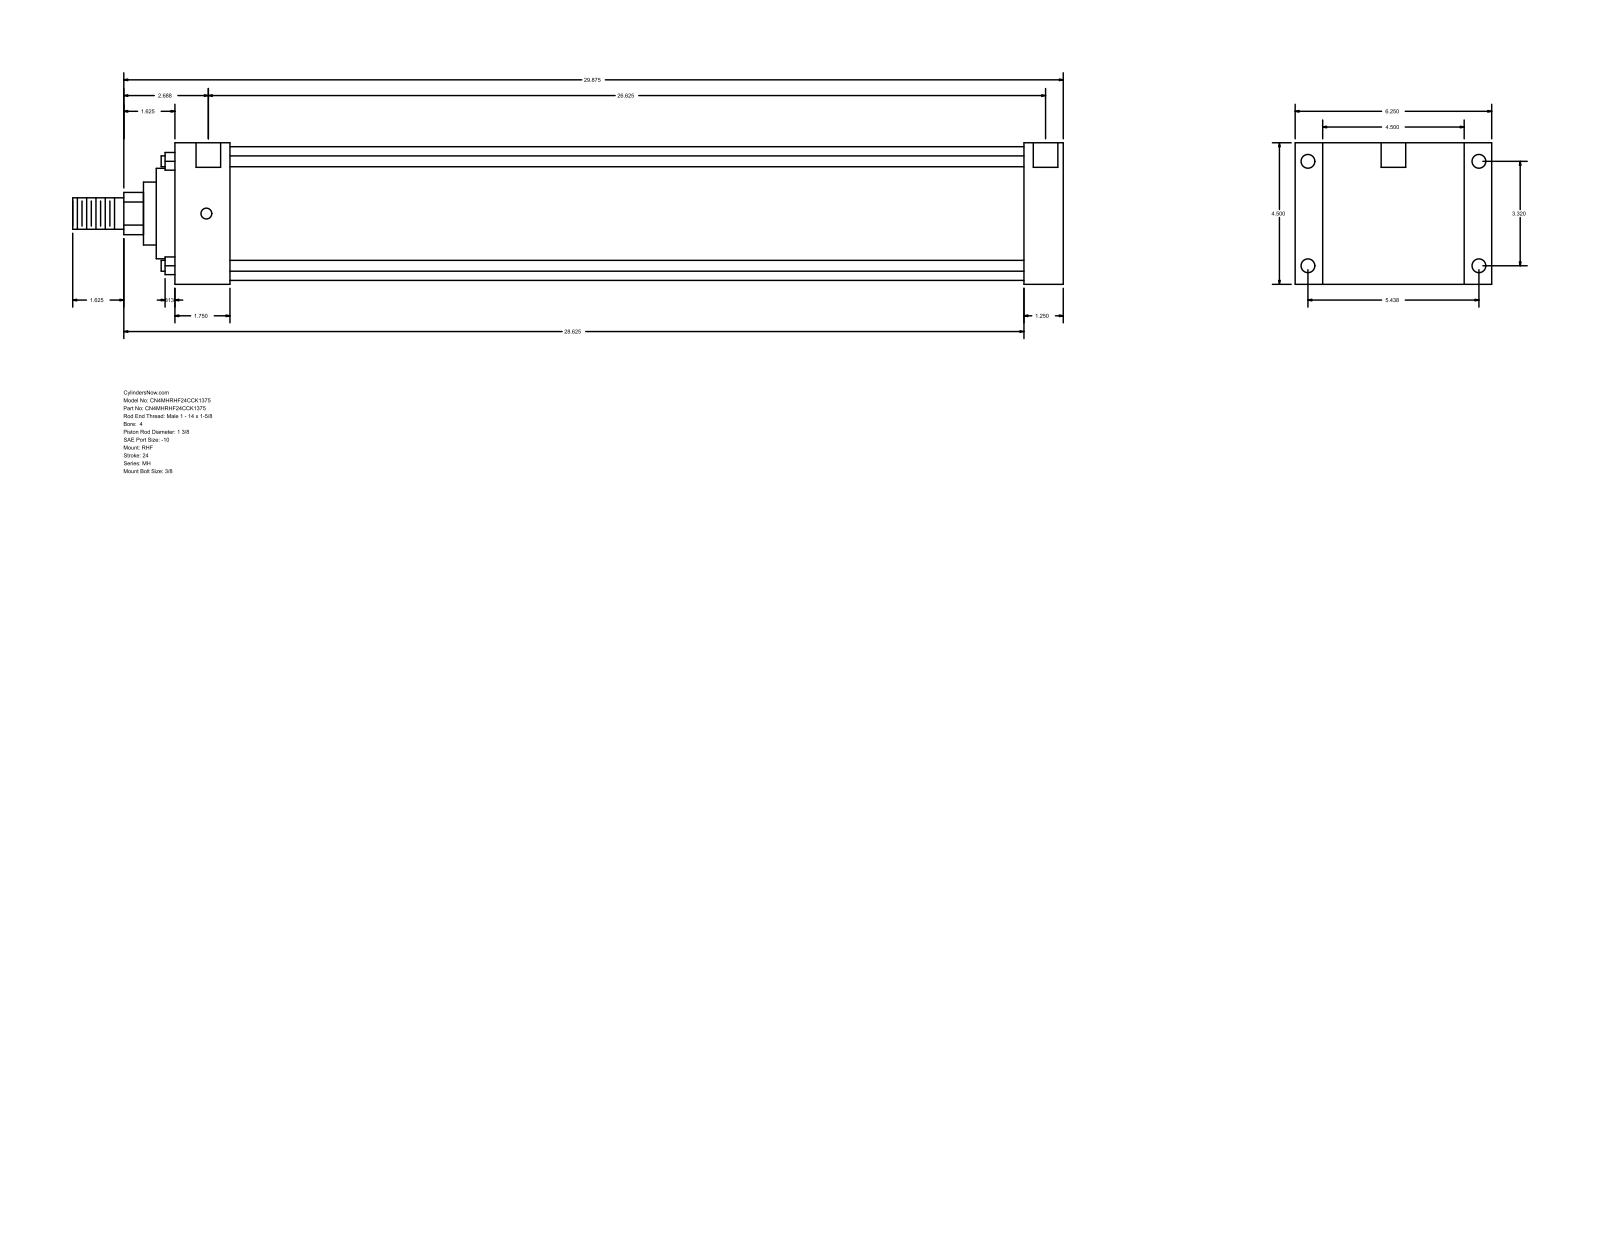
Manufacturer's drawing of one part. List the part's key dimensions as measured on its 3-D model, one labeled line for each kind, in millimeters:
Part name (STEP PRODUCT): MH_RHF__0400_1.375
STEP written by: GSSL Pune (CONFIG_CONTROL_DESIGN)
Units: millimetres
Bodies: 0 solids, 90 faces (61 planar, 29 cylindrical, 0 other)
Overall size (bounding box): 800.1 × 158.75 × 114.3
Round holes (diameter × count): ⌀8.73 ×4, ⌀11.13 ×4, ⌀19.84 ×2
Round bosses / shafts (diameter × count): ⌀8.76 ×4, ⌀107.95 ×1, ⌀73.03 ×1, ⌀50.8 ×1, ⌀34.92 ×1, ⌀25.4 ×1
Partial cylindrical surfaces — rounded edges, fillets, slot ends (radius × count): R17.06 ×1
Main face-to-face distances: 114.3, 31.75, 685.81, 717.56, 22.23, 136.53, 44.45, 641.36, 673.11, 158.76
Hole centre spacings: 84.32, 138.12, 161.82, 679.45, 1.58, 1.59, 676.28, 677.86
